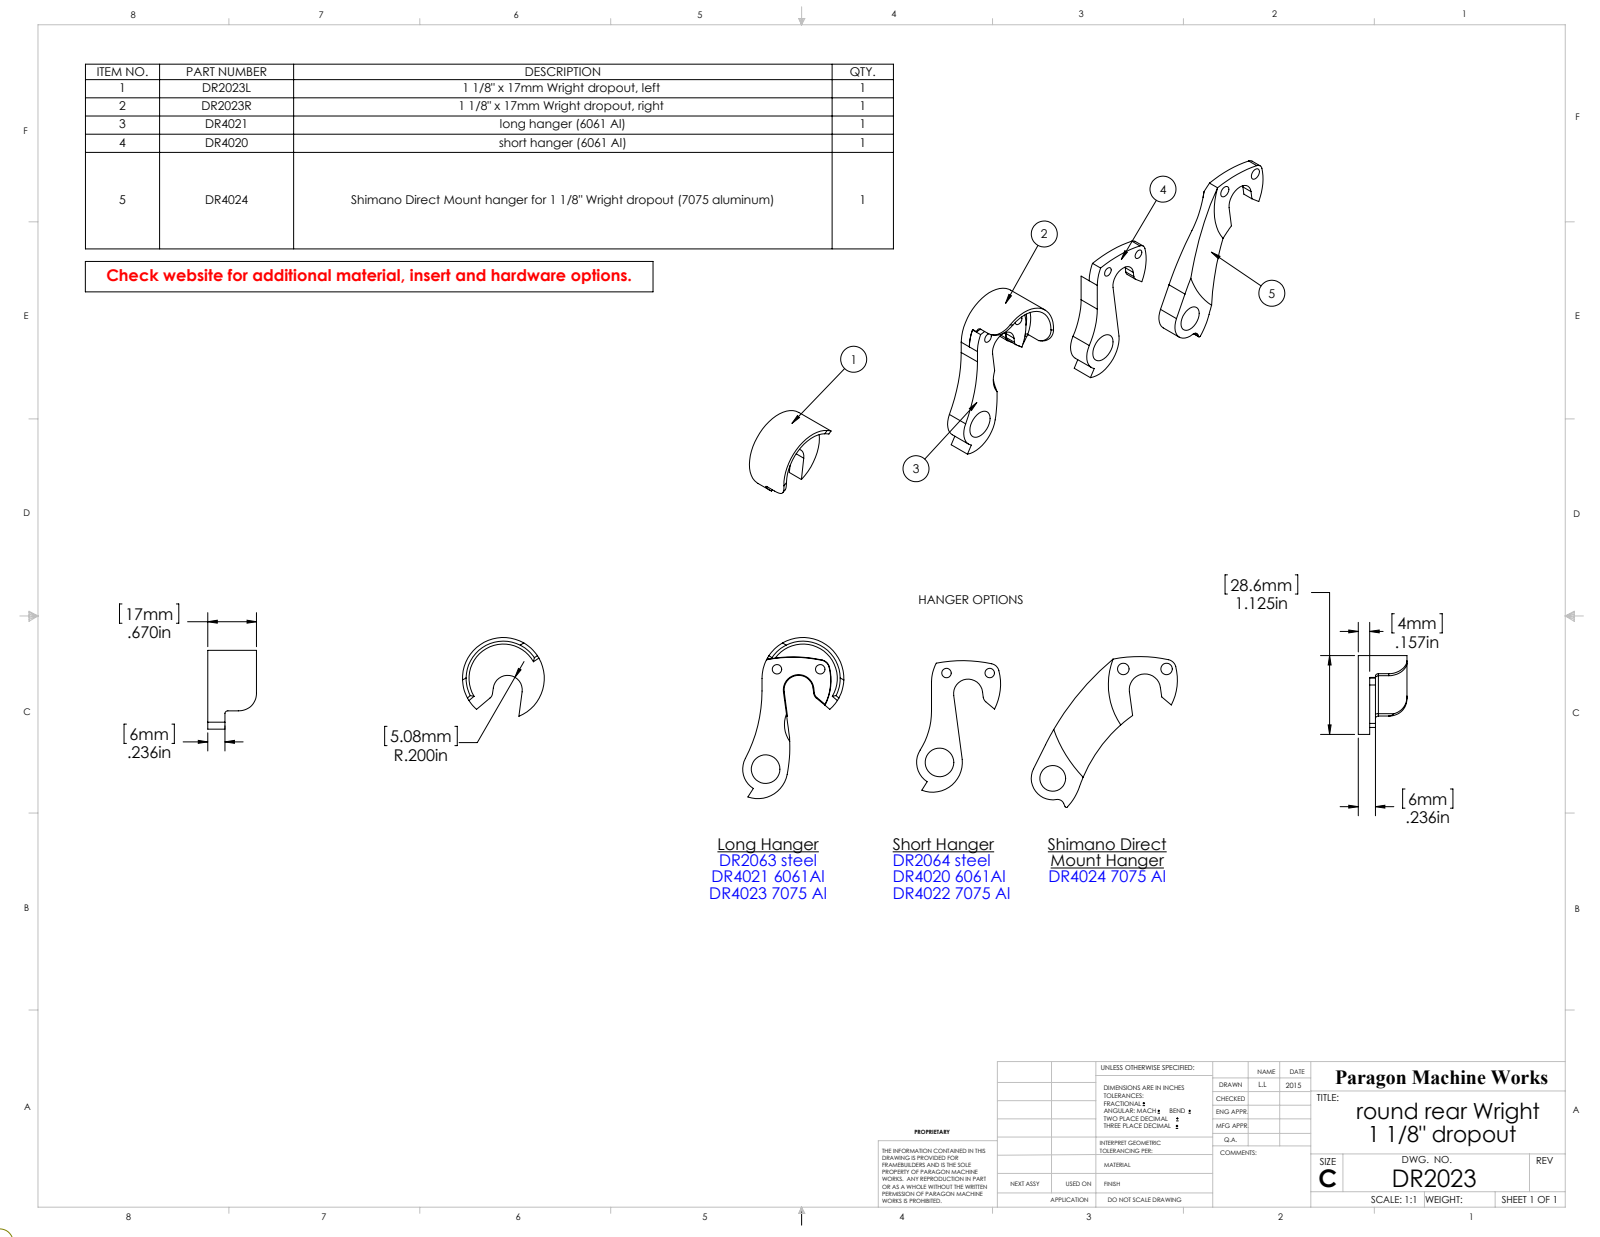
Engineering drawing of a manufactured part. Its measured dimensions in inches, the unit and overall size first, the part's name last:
Units: inches
Overall size (bounding box): 5.244 × 1.083 × 0.67
Round holes (diameter × count): ⌀0.177 ×2
Round bosses / shafts (diameter × count): ⌀1.125 ×2
Partial cylindrical surfaces — rounded edges, fillets, slot ends (radius × count): R0.04 ×4, R0.25 ×4, R0.097 ×2, R0.1 ×2, R0.2 ×2, R0.513 ×2, R0.13 ×1, R0.405 ×1
Main face-to-face distances: 0.236, 0.157, 0.079, 0.15, 0.086, 0.67, 0.52, 0.513, 0.434, 0.4
Hole centre spacings: 0.594
Volume: 0.349 in³ · Surface area: 7.984 in²
Bodies: 2 solids, 64 faces (19 planar, 37 cylindrical, 8 other)
Part name (STEP PRODUCT): DR2023R; DR2023; DR2023L
STEP written by: SolidWorks 2015 (AUTOMOTIVE_DESIGN)
